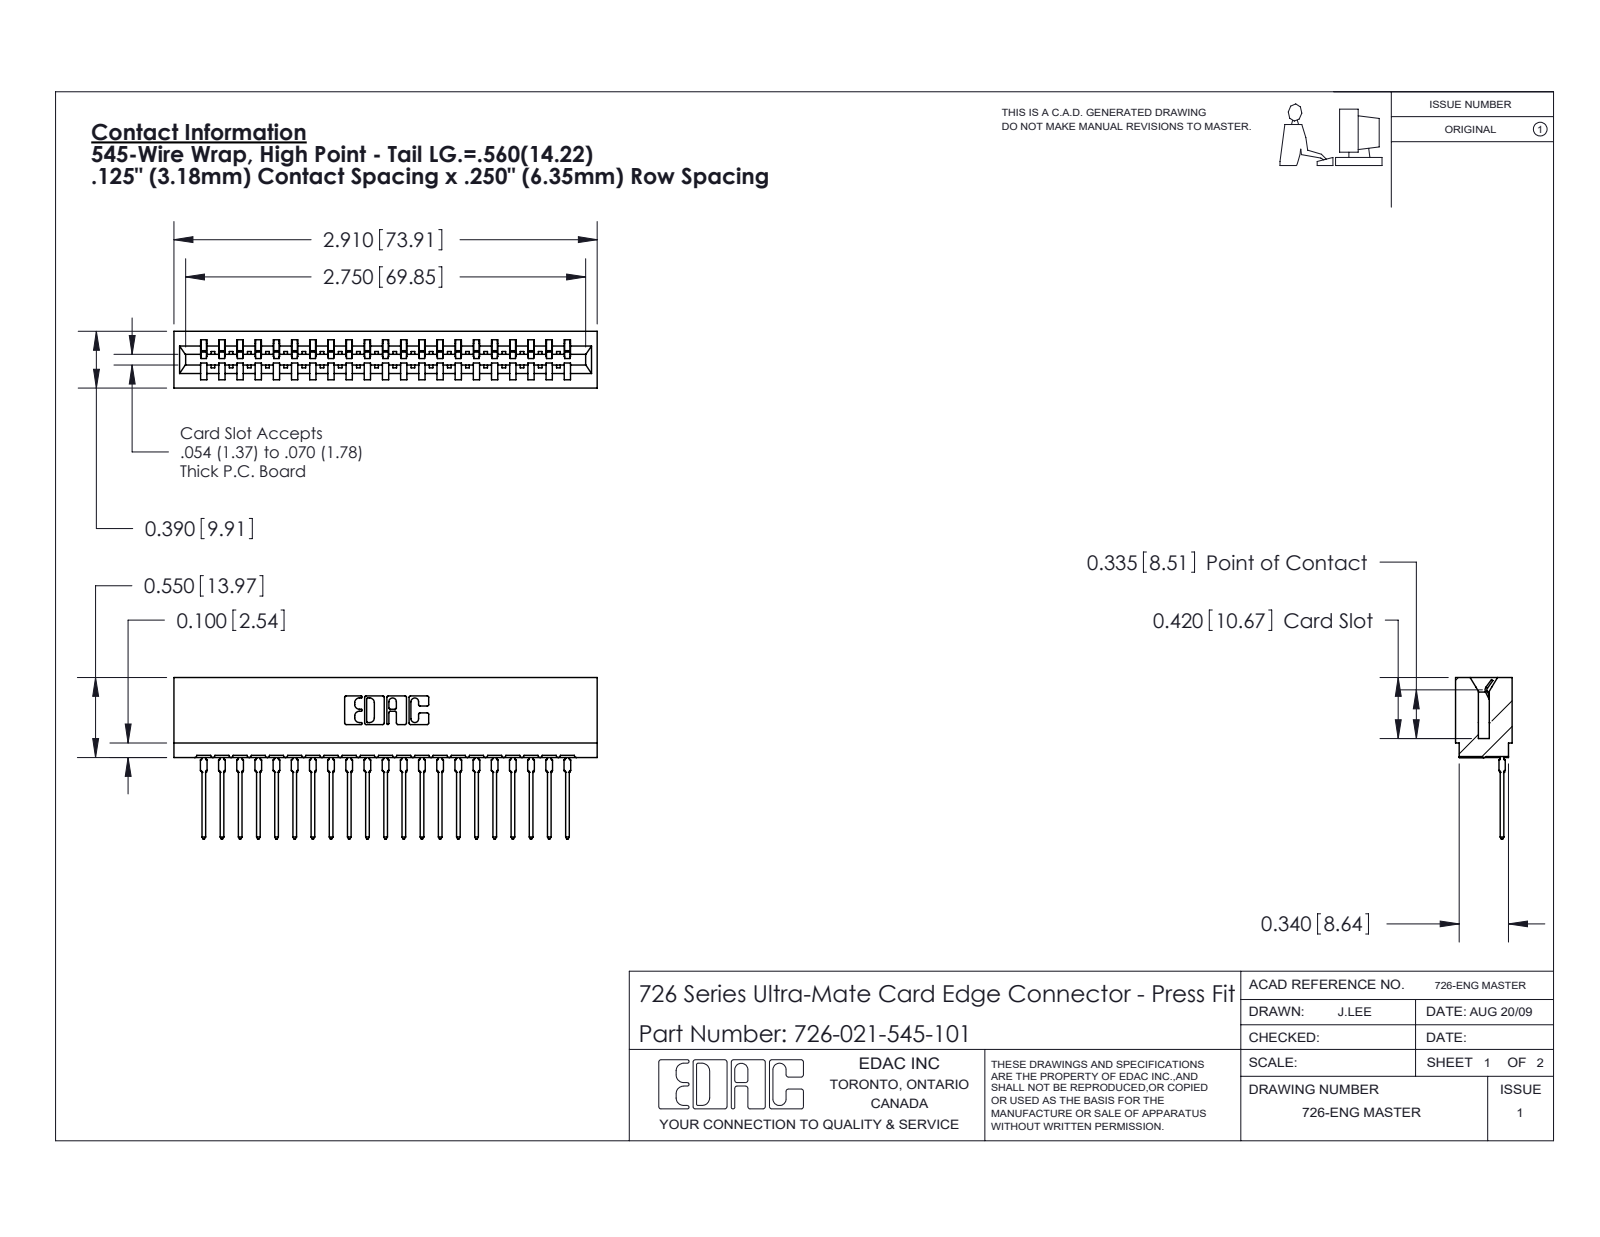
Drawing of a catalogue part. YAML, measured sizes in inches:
part_name: "726-021-545-101; 726 Part_.515 Slot Depth - 01; 746-292-001_545"
step_written_by: "SolidWorks 2020 (CONFIG_CONTROL_DESIGN)"
units: inches
bodies: {solids: 22, faces: 2365, planar: 1378, cylindrical: 441, other: 546}
overall_size: [2.91, 1.109, 0.39]
volume: 0.414
surface_area: 16.01
partial_cylinders:
  - {radius: 0.021, count: 42}
  - {radius: 0.01, count: 22}
  - {radius: 0.015, count: 22}
  - {radius: 0.007, count: 6}
  - {radius: 0.031, count: 6}
  - {radius: 0.005, count: 4}
  - {radius: 0.011, count: 4}
  - {radius: 0.026, count: 3}
face_to_face_distances: [0.057, 0.333, 0.39, 0.25, 0.025, 0.307, 0.083, 0.5, 0.75, 0.042]
